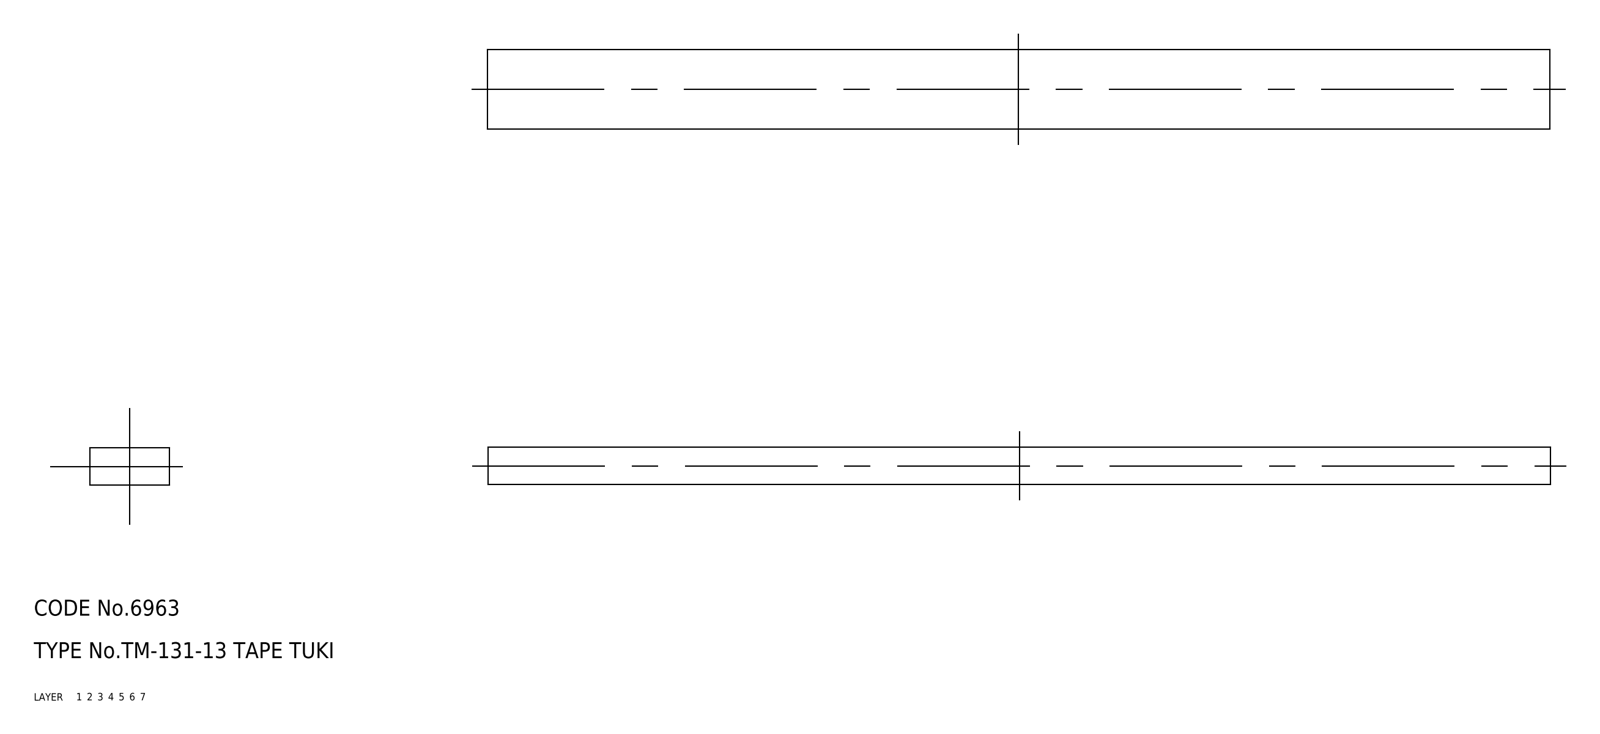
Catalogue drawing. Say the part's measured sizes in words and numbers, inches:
The part is named "rubber foam". Its 3-D file was written by "CADfix (AUTOMOTIVE_DESIGN)". It is 1 solid with 6 faces: 0 planar, 0 cylindrical and 6 other. Overall it measures 7.874 by 0.591 by 0.276 inches. Its volume is 1.281 cubic inches and its surface area 13.97 square inches.
